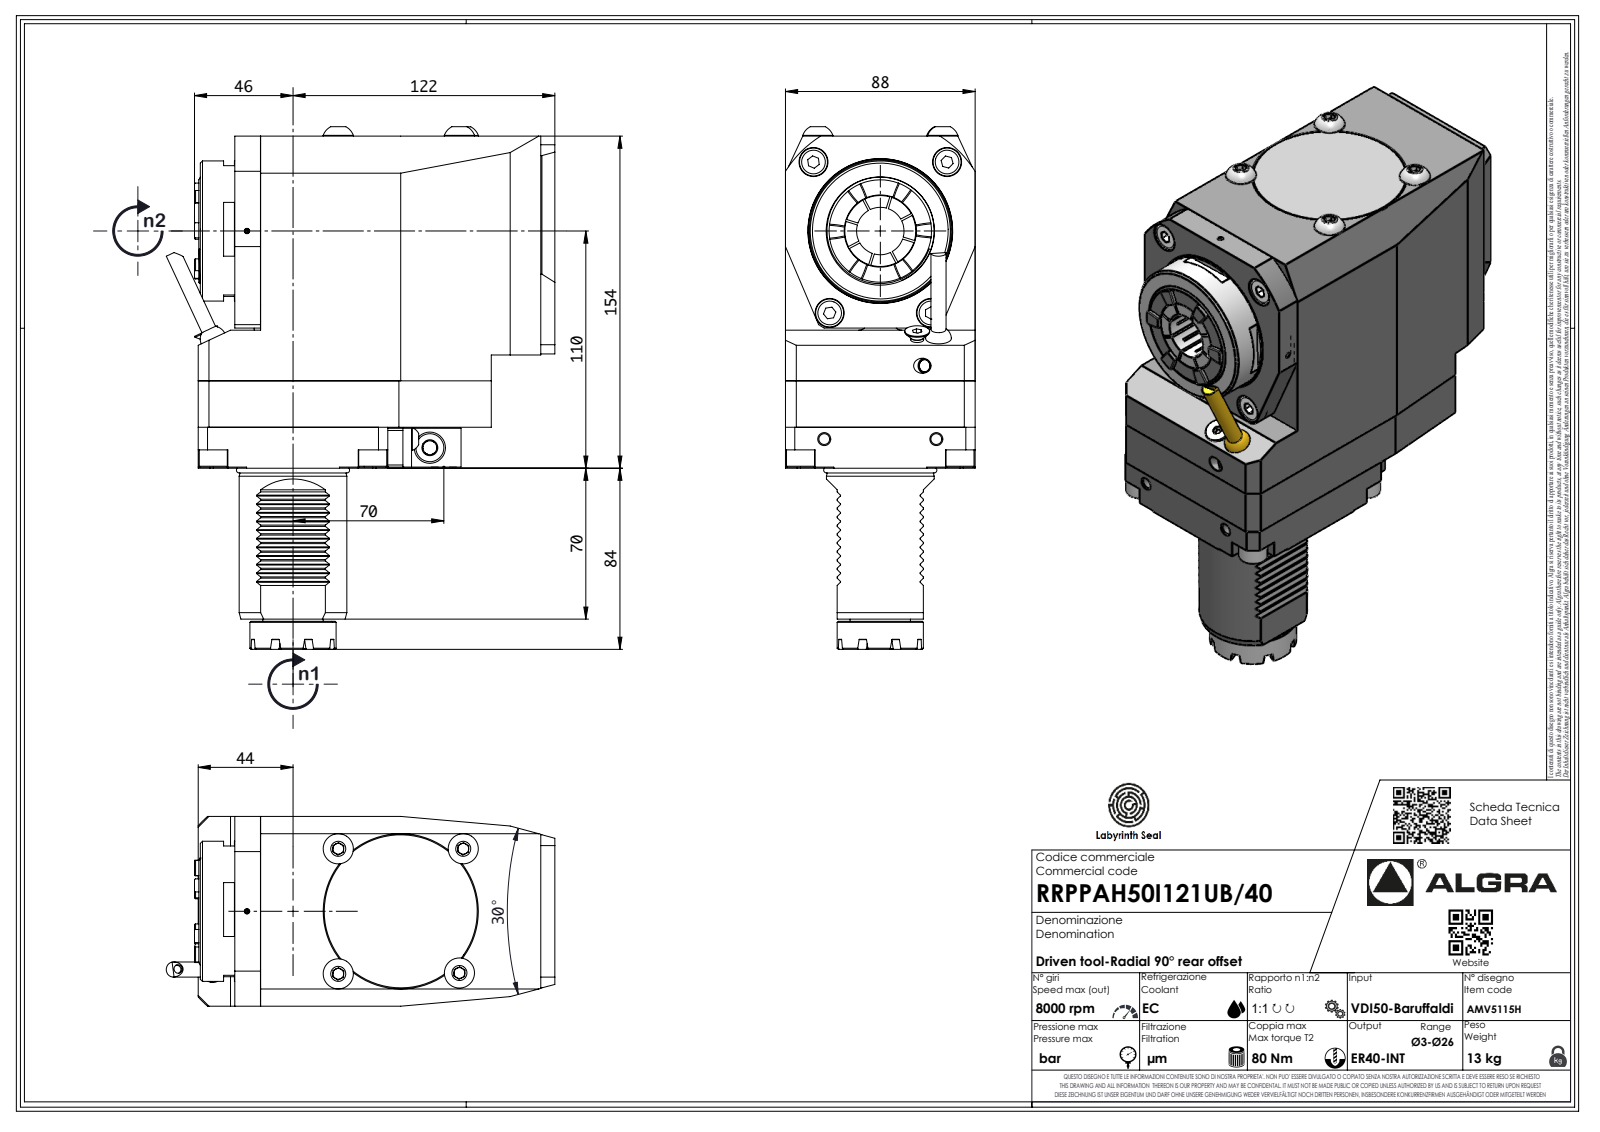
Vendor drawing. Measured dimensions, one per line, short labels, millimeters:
name: RRPPAH50I121UB40
written by: SolidWorks 2023 (AUTOMOTIVE_DESIGN)
unit: mm
bodies: 1 solid, 683 faces (461 planar, 114 cylindrical, 108 other)
size: 242.4 × 180.32 × 88
volume: 2 016 000 mm³; area: 120 556 mm²
holes: 1× ⌀2.1, 1× ⌀10
bosses: 4× ⌀14, 4× ⌀13, 1× ⌀65, 1× ⌀50, 1× ⌀48.7, 1× ⌀40, 1× ⌀28, 1× ⌀7
rounds: 22× R0.3, 16× R0.2, 7× R0.33, 7× R0.52, 7× R3.7, 4× R1, 4× R6.75, 2× R4
face distances: 88, 135, 154, 1, 165.5, 19, 0.5, 17, 148.5, 18.5
